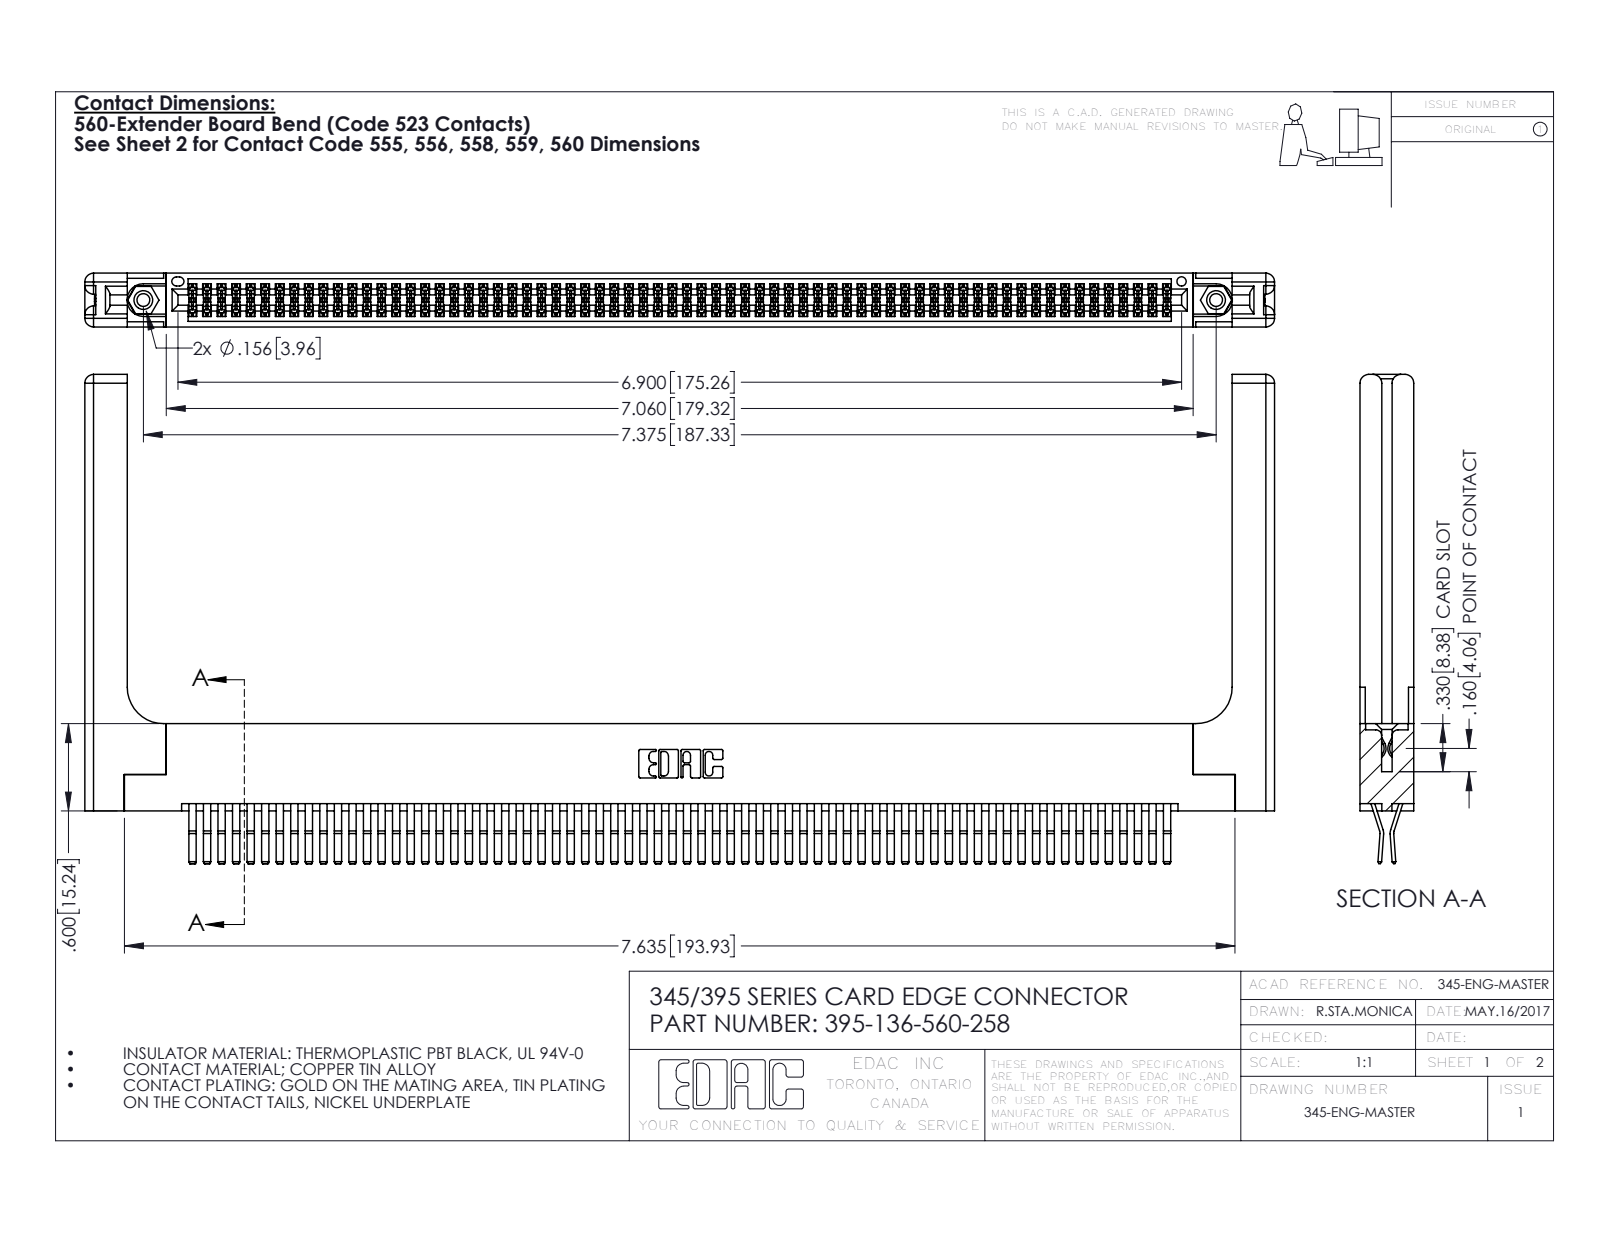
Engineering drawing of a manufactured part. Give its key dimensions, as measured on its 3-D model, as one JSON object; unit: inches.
{"part_name": "395-136-560-258; 345 Part_Flush Mounting Lugs - 0.156 Dia-TH; 345-250-001_345-250-001-102; 345-292-001_560 Tail (+1 more)", "step_written_by": "SolidWorks 2016 (CONFIG_CONTROL_DESIGN)", "units": "inches", "bodies": {"solids": 141, "faces": 7454, "planar": 4716, "cylindrical": 2678, "other": 60}, "overall_size": [8.179, 3.362, 0.37], "volume_in3": 1.818, "surface_area_in2": 61.01, "round_holes": [[0.089, 2], [0.125, 2], [0.156, 2], [0.064, 1]], "round_bosses_or_shafts": [[0.155, 2]], "partial_cylinders_radius": [[0.006, 204], [0.01, 22], [0.06, 16], [0.007, 6], [0.031, 6], [0.026, 3], [0.01, 2], [0.014, 2]], "face_to_face_distances": [0.072, 0.298, 0.025, 0.37, 0.2, 0.098, 0.272, 0.225, 0.148, 0.15], "hole_center_spacings": [0.27, 7.139, 7.375]}
